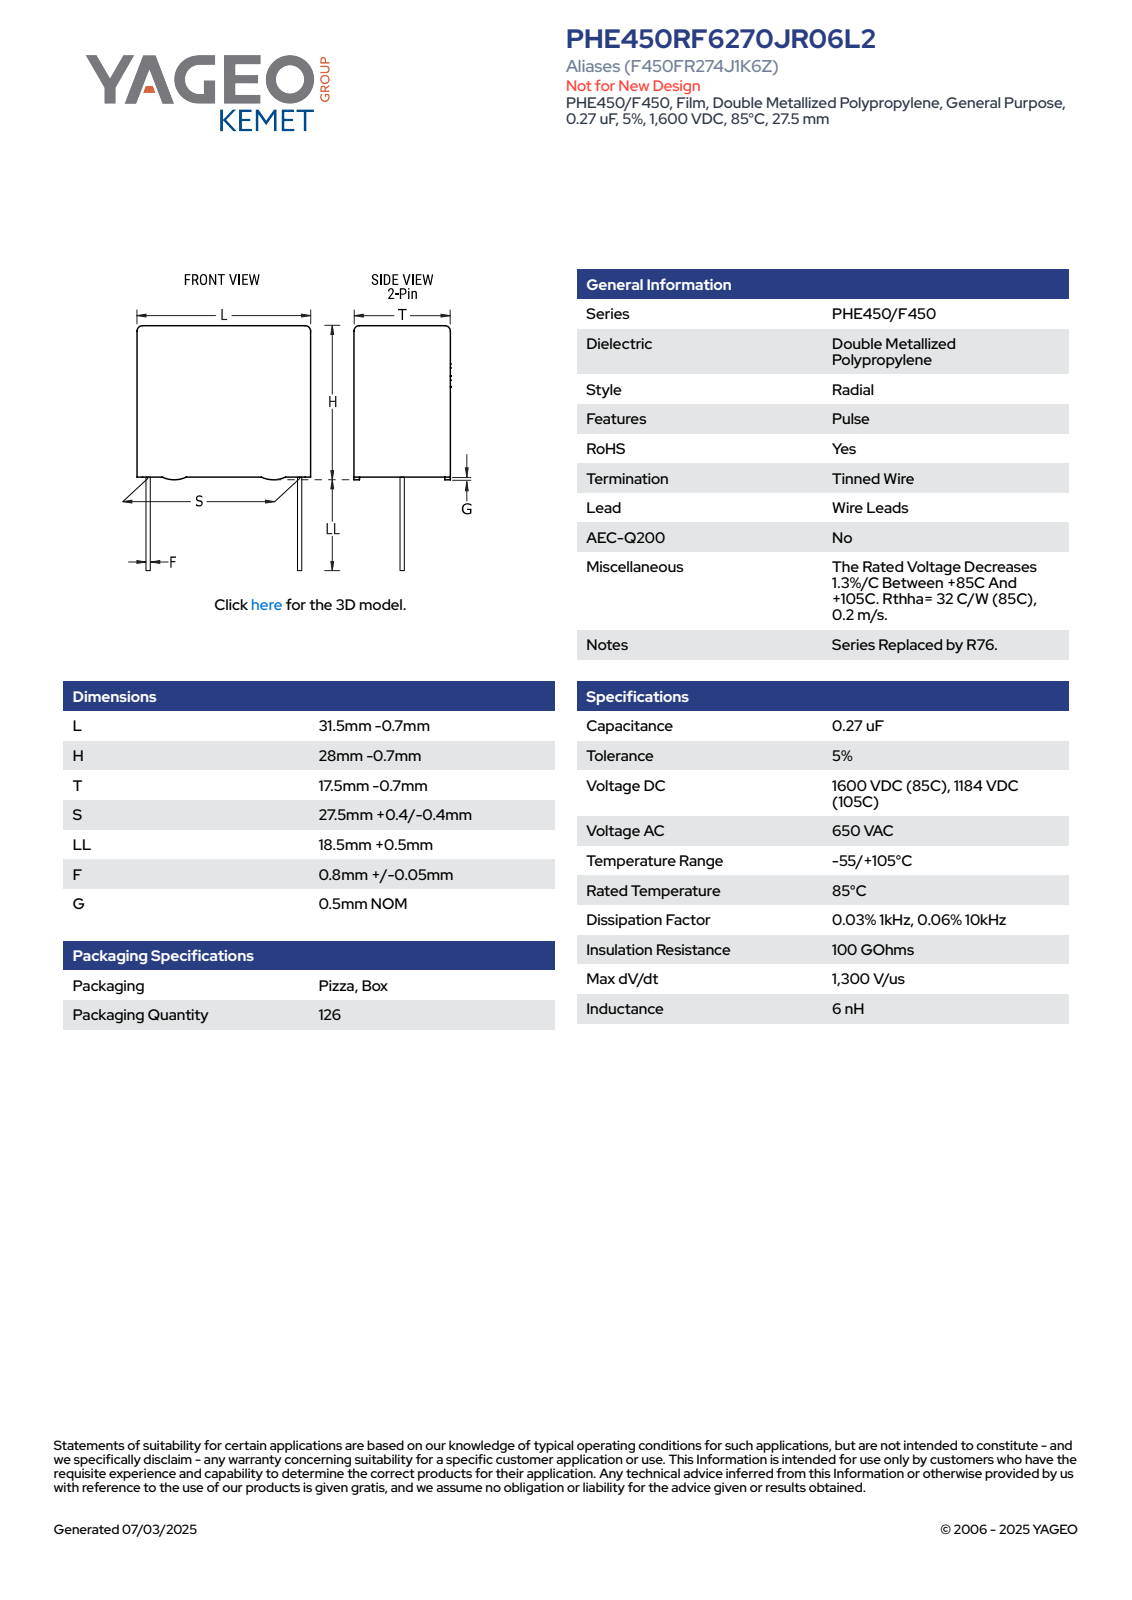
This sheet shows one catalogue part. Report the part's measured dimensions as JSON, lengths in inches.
{"part_name": "CFR_RBG_31.5X28X17.5_L31.5H28T17.5S27.5LL19F0.85G0.5", "step_written_by": "SolidWorks 2014 (AUTOMOTIVE_DESIGN)", "units": "inches", "bodies": {"solids": 4, "faces": 89, "planar": 81, "cylindrical": 8, "other": 0}, "overall_size": [1.85, 1.24, 0.689], "volume_in3": 0.927, "surface_area_in2": 6.216, "round_bosses_or_shafts": [[0.033, 2]], "partial_cylinders_radius": [[0.02, 4]], "face_to_face_distances": [0.689, 1.083, 1.24, 0.689, 0.02, 1.102, 0.039, 0.65, 0.04, 0.61]}
